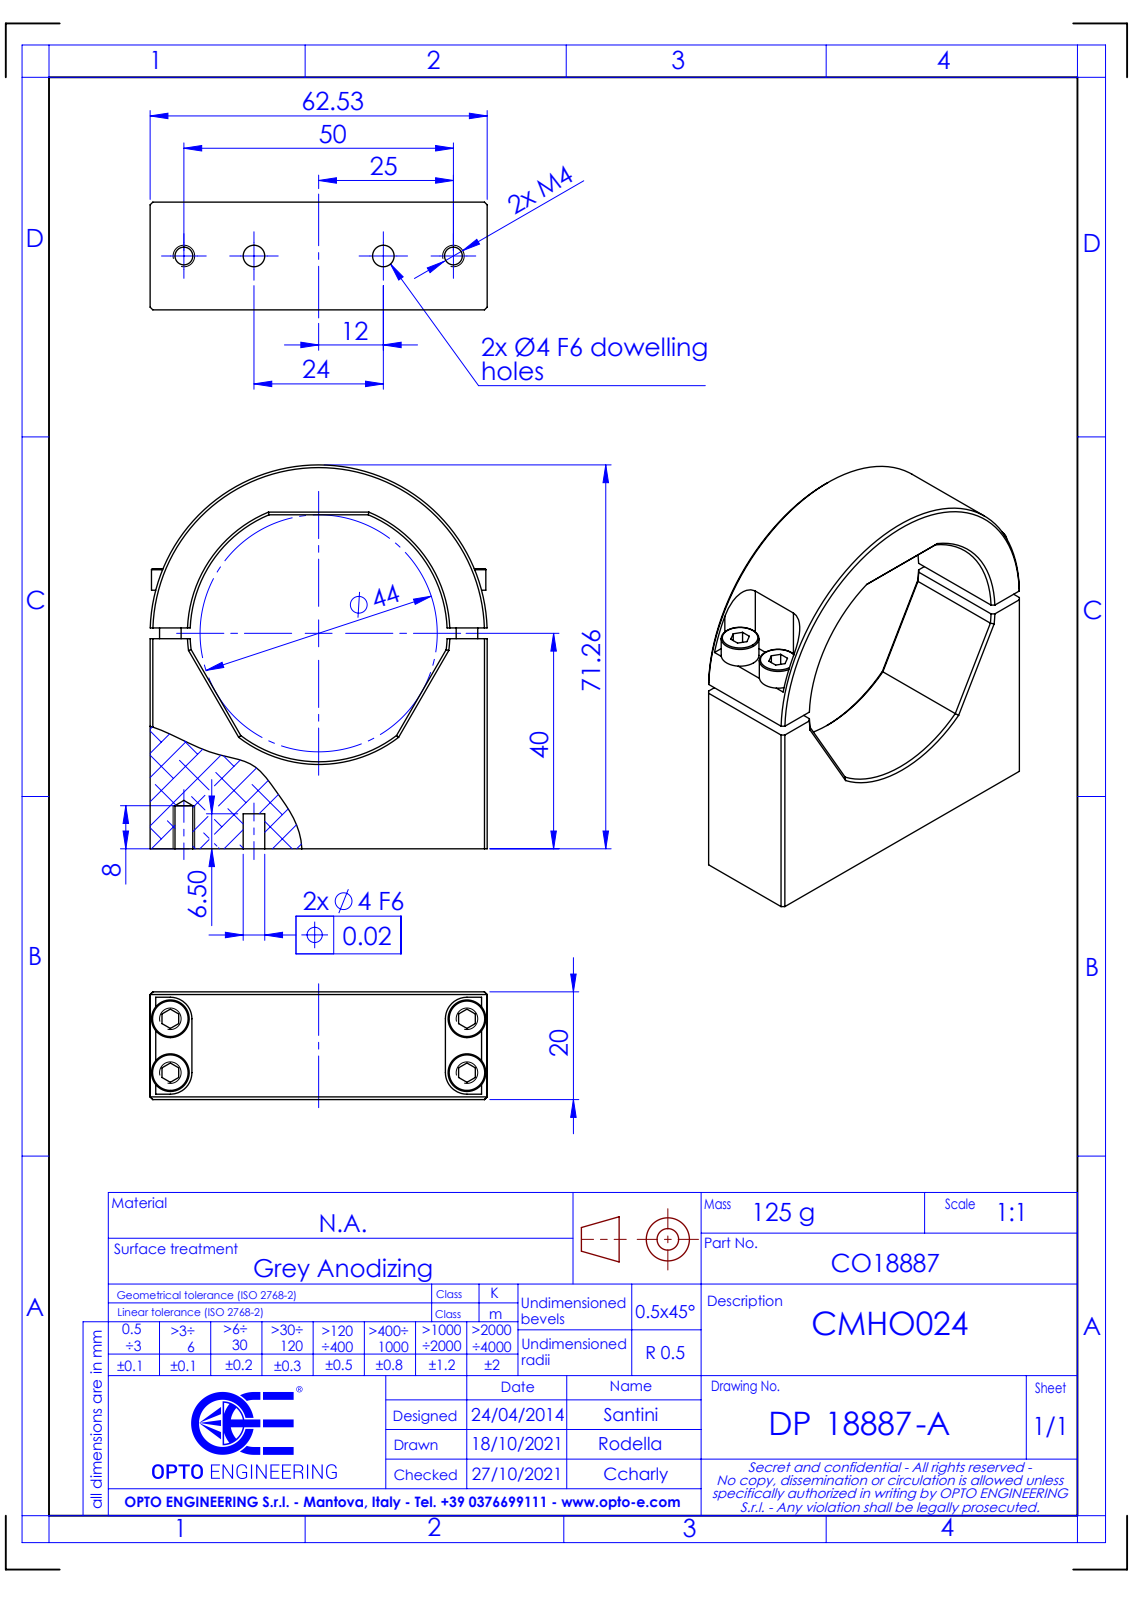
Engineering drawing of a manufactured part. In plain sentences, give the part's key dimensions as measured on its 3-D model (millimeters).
The part is named "DP18887-A_CMHO024". Its 3-D file was written by "SolidWorks 2021 (CONFIG_CONTROL_DESIGN)". It is 0 solids with 122 faces: 60 planar, 42 cylindrical and 20 other. Overall it measures 71.26 by 62.53 by 20 millimeters. Round holes: 4 of diameter 4.5, 2 of diameter 3.3, 2 of diameter 4. Round bosses or shafts: 4 of diameter 7, 4 of diameter 4. Partial cylindrical surfaces (rounded edges, fillets, slot ends): 4 of radius 4, 1 of radius 23.85, 1 of radius 31.26. The main face-to-face distances are 20, 62.52, 62, 39, 23, 48, 9, 14, 7.75, 54.77. The hole center spacings are 5.59, 16.3, 39.83, 52.75, 10, 13, 37, 55.02.
